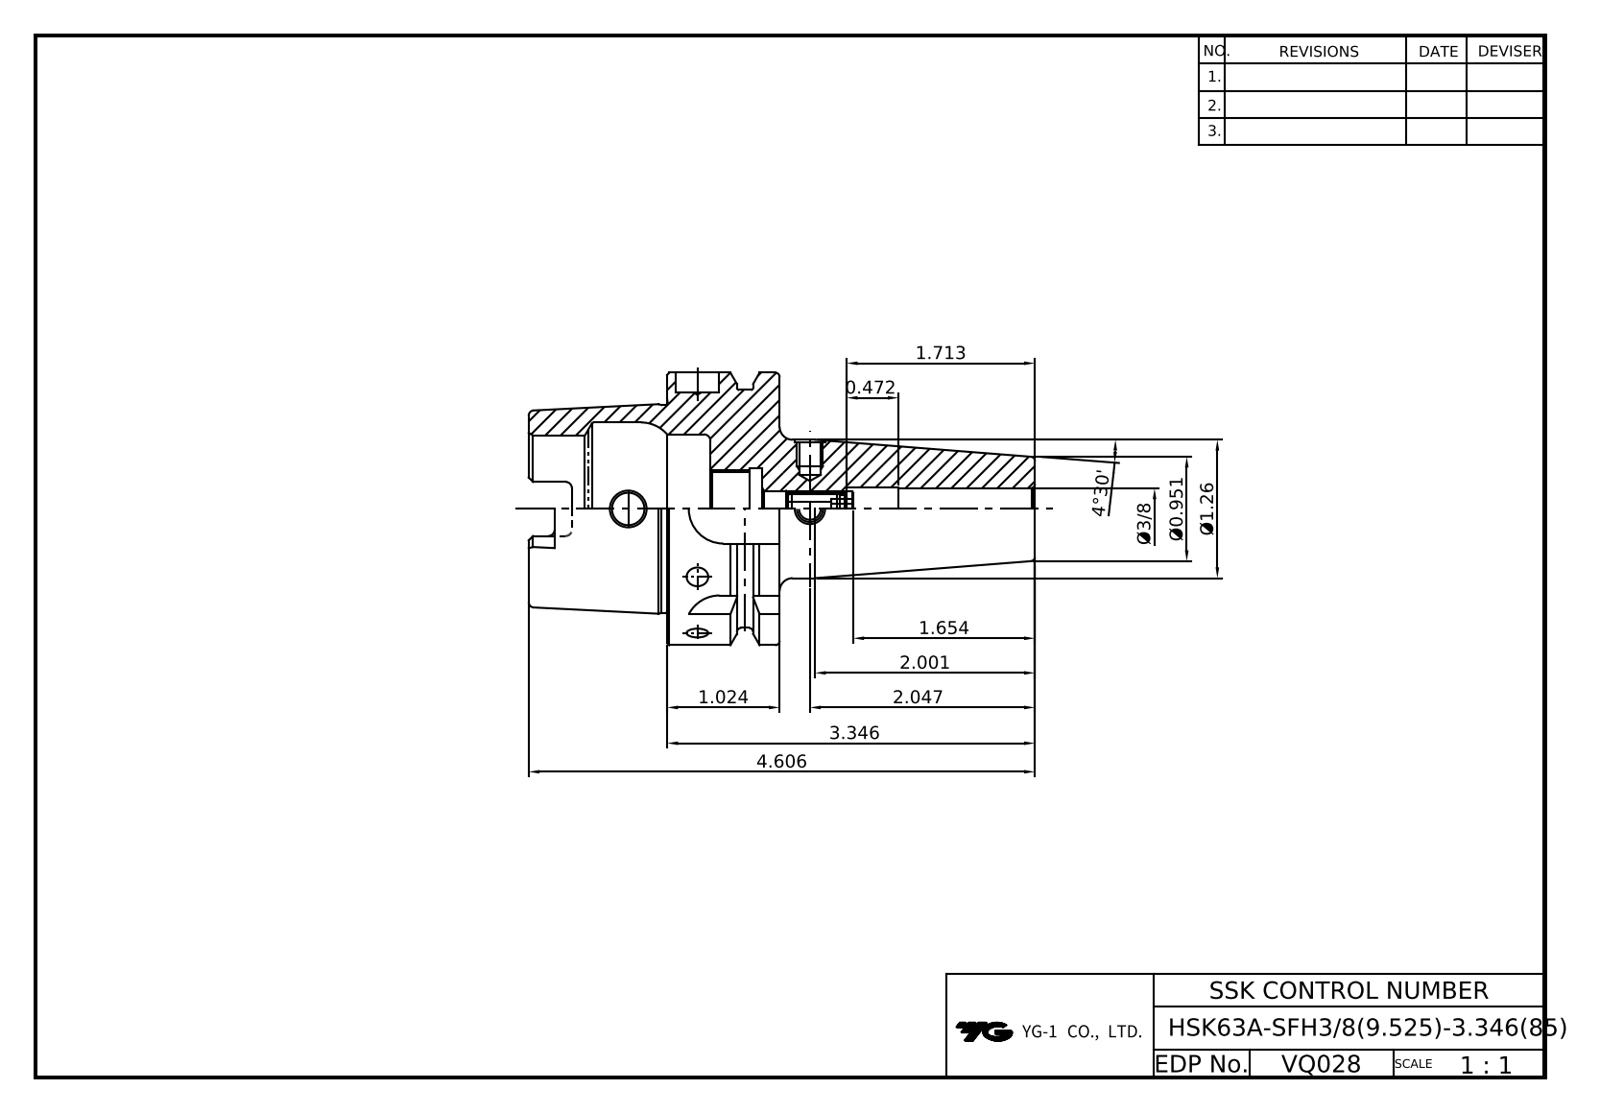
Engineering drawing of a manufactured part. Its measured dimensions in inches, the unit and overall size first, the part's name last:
Units: inches
Overall size (bounding box): 4.606 × 2.48 × 2.48
Round holes (diameter × count): ⌀0.197 ×2, ⌀0.276 ×2, ⌀0.28 ×1, ⌀0.295 ×1, ⌀0.33 ×1, ⌀0.374 ×1, ⌀0.394 ×1, ⌀0.398 ×1, ⌀0.669 ×1, ⌀0.709 ×1, ⌀0.748 ×1, ⌀1.339 ×1
Round bosses / shafts (diameter × count): ⌀2.48 ×1, ⌀2.165 ×1, ⌀1.891 ×1, ⌀1.26 ×1
Partial cylindrical surfaces — rounded edges, fillets, slot ends (radius × count): R0.059 ×6, R0.113 ×4, R0.315 ×4
Main face-to-face distances: 1.024, 0.394, 0.63, 1.26, 1.654, 2.283, 2.087, 0.157, 4.606, 3.346
Hole centre spacings: 1.023, 1.653
Volume: 7.016 in³ · Surface area: 46.21 in²
Bodies: 1 solid, 206 faces (61 planar, 67 cylindrical, 78 other)
Part name (STEP PRODUCT): VQ028-HSK63A-SFH0_375-3_346
STEP written by: PRO/ENGINEER BY PARAMETRIC TECHNOLOGY CORPORATION, 2012130 (CONFIG_CONTROL_DESIGN)
